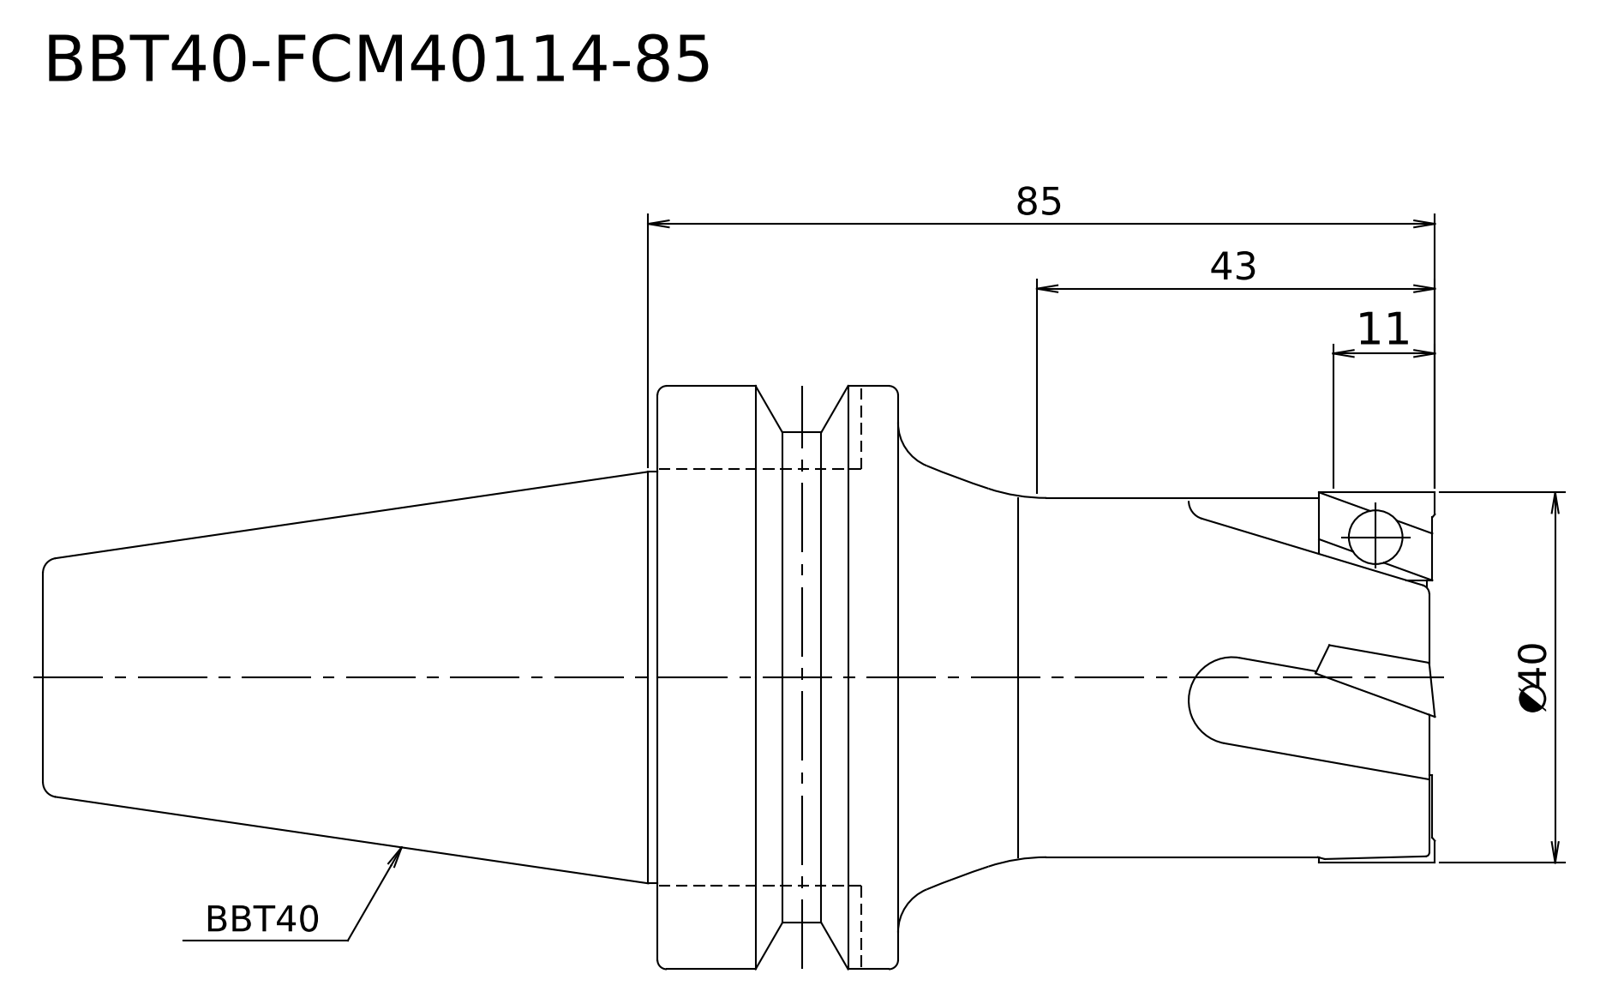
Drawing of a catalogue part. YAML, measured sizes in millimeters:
step_written_by: "Kubotek KeyCreator V8.5.1 (14335) (CONFIG_CONTROL_DESIGN)"
units: millimeters
bodies: {solids: 1, faces: 17, planar: 4, cylindrical: 6, other: 7}
overall_size: [150.4, 63, 63]
volume: 214524
surface_area: 25247
round_bosses_or_shafts:
  - {diameter: 63, count: 1}
  - {diameter: 53, count: 1}
  - {diameter: 44.45, count: 1}
  - {diameter: 40, count: 1}
  - {diameter: 38.8, count: 1}
face_to_face_distances: [84, 58, 26, 150.4, 92.4, 66.4]
